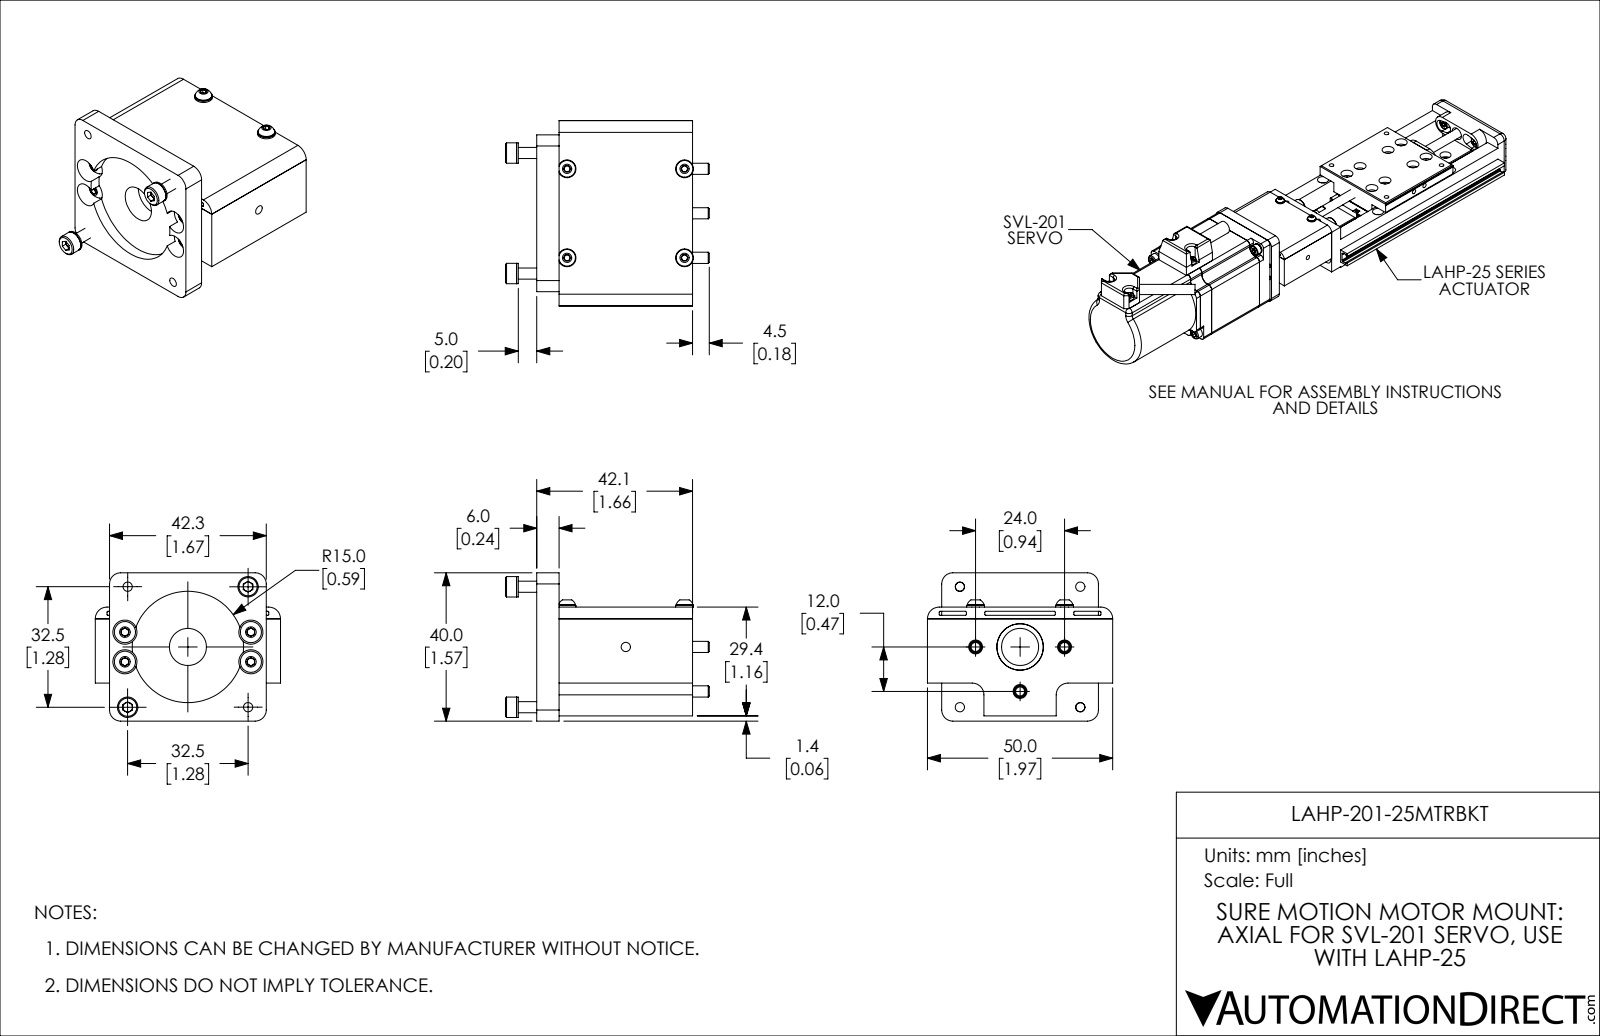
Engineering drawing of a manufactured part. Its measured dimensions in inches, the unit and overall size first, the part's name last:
Units: inches
Overall size (bounding box): 2.165 × 1.969 × 1.575
Round holes (diameter × count): ⌀0.098 ×9, ⌀0.126 ×9, ⌀0.148 ×7, ⌀0.256 ×7, ⌀0.081 ×4, ⌀0.106 ×4, ⌀0.122 ×4, ⌀0.394 ×1, ⌀0.493 ×1, ⌀1.182 ×1
Round bosses / shafts (diameter × count): ⌀0.217 ×9, ⌀0.118 ×9, ⌀0.224 ×4, ⌀0.189 ×4, ⌀0.177 ×4, ⌀0.098 ×4, ⌀0.492 ×1
Partial cylindrical surfaces — rounded edges, fillets, slot ends (radius × count): R0.01 ×12, R0.125 ×12, R0.118 ×4
Main face-to-face distances: 0.125, 0.118, 0.236, 0.08, 0.045, 1.42, 0.682, 0.762, 0.807, 1.656
Hole centre spacings: 0.661, 1.283, 0.252, 0.483, 0.687, 0.798, 0.905, 1.152
Volume: 2.047 in³ · Surface area: 36.84 in²
Bodies: 29 solids, 640 faces (277 planar, 215 cylindrical, 148 other)
Part name (STEP PRODUCT): LAHP-201-25MTRBKT
STEP written by: SolidWorks 2019 (CONFIG_CONTROL_DESIGN)
